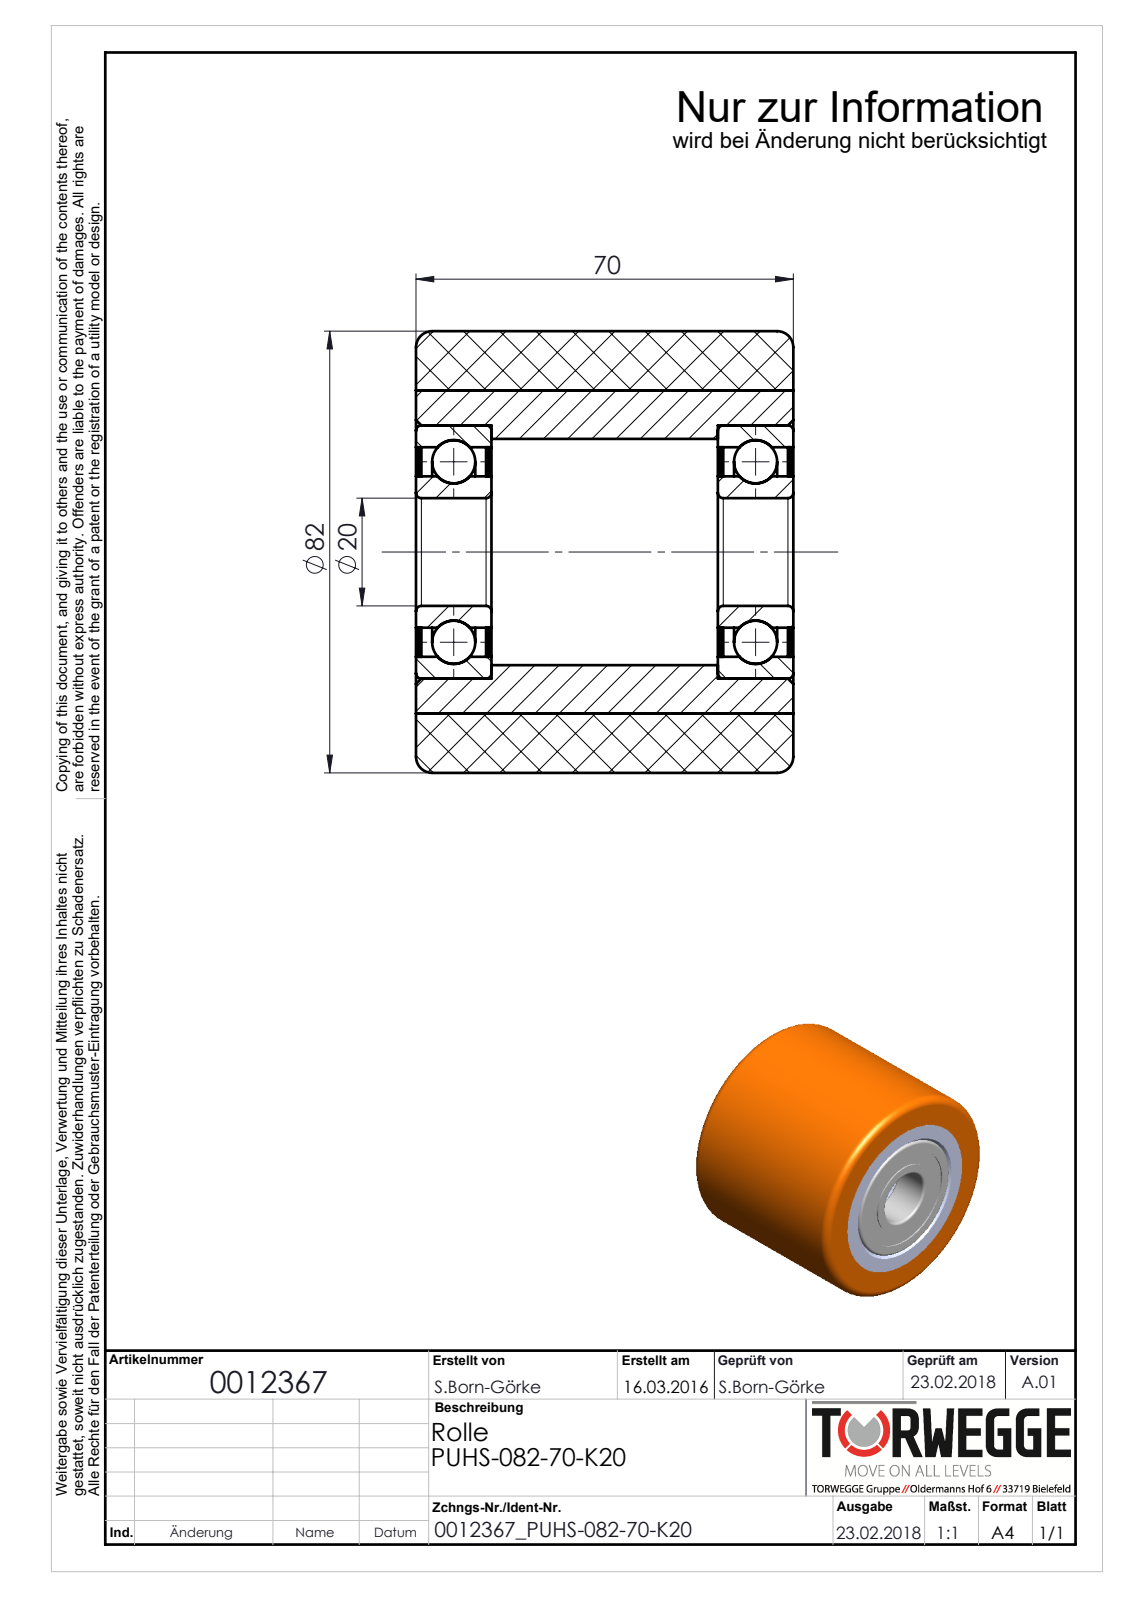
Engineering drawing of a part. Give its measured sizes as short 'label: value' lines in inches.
name: 0012367_PUHS-082-70-K20
written by: SolidWorks 2016 (AUTOMOTIVE_DESIGN)
unit: in
bodies: 12 solids, 118 faces (22 planar, 52 cylindrical, 44 other)
size: 3.228 × 3.228 × 2.756
volume: 17.98 in³; area: 134.1 in²
holes: 1× ⌀0.787, 1× ⌀1.106, 1× ⌀1.531, 1× ⌀1.654, 1× ⌀1.85, 1× ⌀2.362
bosses: 1× ⌀3.228
face distances: 0.02, 2.205, 0.512, 2.756, 0.039, 0.531, 2.224, 0.492, 2.185, 0.551
